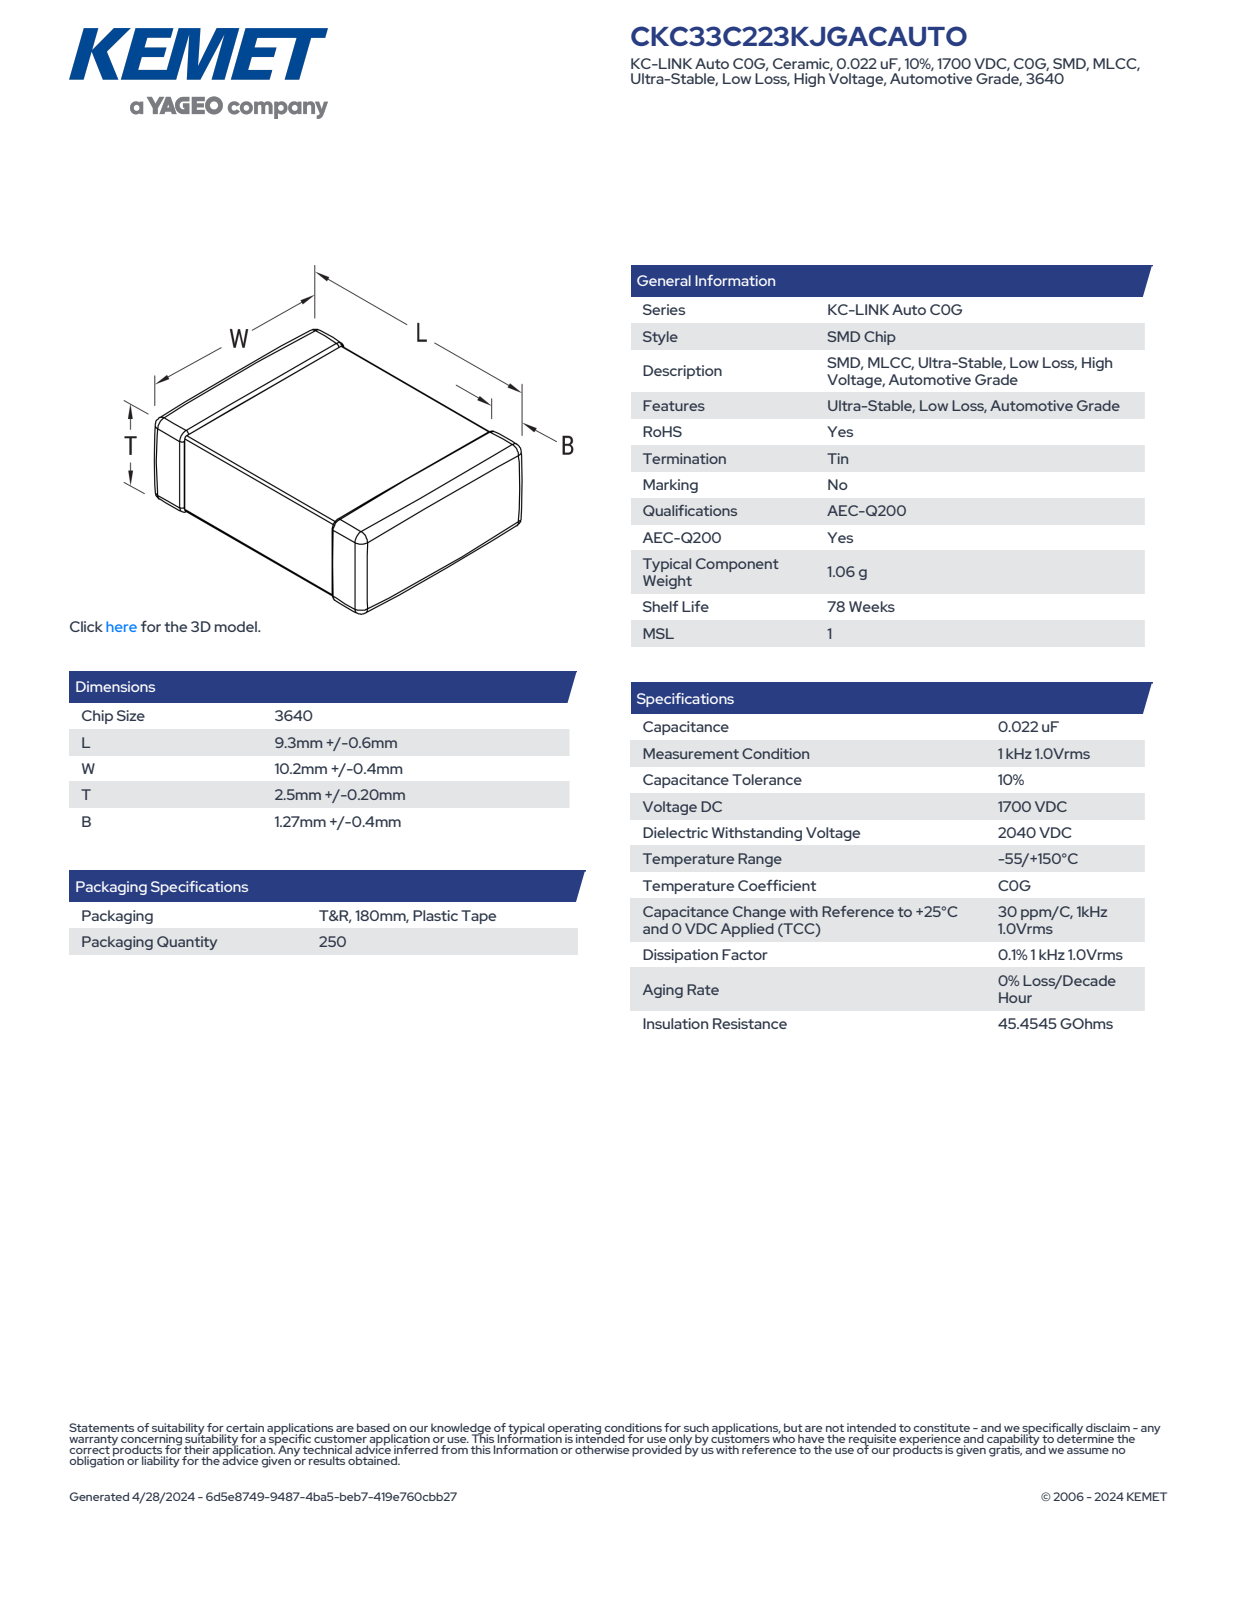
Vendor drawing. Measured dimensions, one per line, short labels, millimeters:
name: CCS_CCSTD_3640_L9.9W10.6T2.7B1.27
written by: SolidWorks 2021 (AUTOMOTIVE_DESIGN)
unit: mm
bodies: 4 solids, 125 faces (71 planar, 38 cylindrical, 16 other)
size: 10.6 × 9.9 × 2.7
volume: 245 mm³; area: 321 mm²
rounds: 24× R0.22
face distances: 2.26, 2.48, 2.7, 9.9, 10.16, 10.38, 10.6, 3.79, 6.11, 5.35
